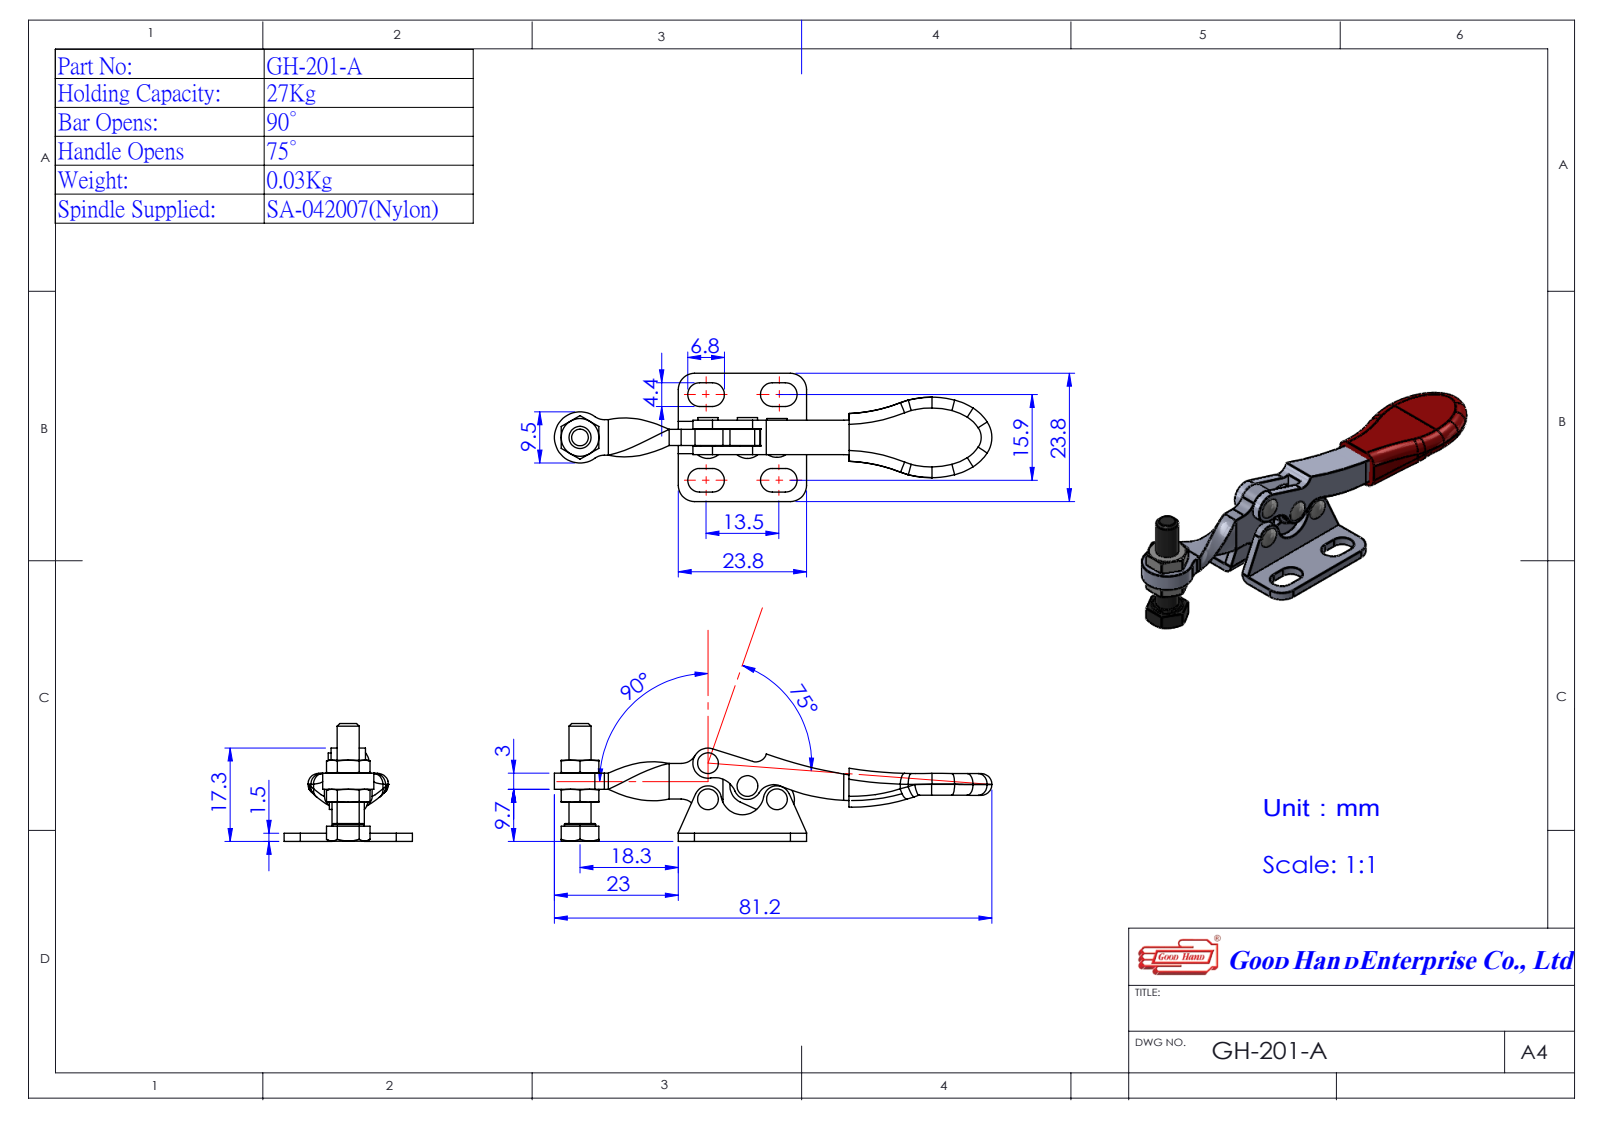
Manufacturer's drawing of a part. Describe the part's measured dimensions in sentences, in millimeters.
The part is named "Group1^EMC201A; 1201A05-1^EMC201A; 1201A08-1^EMC201A; Group5^EMC201A (+2 more)". Its 3-D file was written by "SolidWorks 2016 (AUTOMOTIVE_DESIGN)". It is 4 solids with 240 faces: 85 planar, 105 cylindrical and 50 other. Overall it measures 81.21 by 23.8 by 21.86 millimeters. Its volume is 2 386 cubic millimeters and its surface area 5 290 square millimeters. Round holes: 4 of diameter 2.5, 1 of diameter 4.3. Round bosses or shafts: 4 of diameter 3.75, 1 of diameter 5.8, 1 of diameter 4.1. Partial cylindrical surfaces (rounded edges, fillets, slot ends): 8 of radius 2.2, 8 of radius 3, 4 of radius 12.23, 2 of radius 2.5, 2 of radius 2.8, 2 of radius 3.25, 2 of radius 4, 2 of radius 8.67. The main face-to-face distances are 1.5, 3, 1.7, 4.7, 6.2, 4.5, 4.8, 6.4, 4.04, 1.6. The hole center spacings are 6, 6.7, 7.73, 8.47, 12.8, 14.45.
